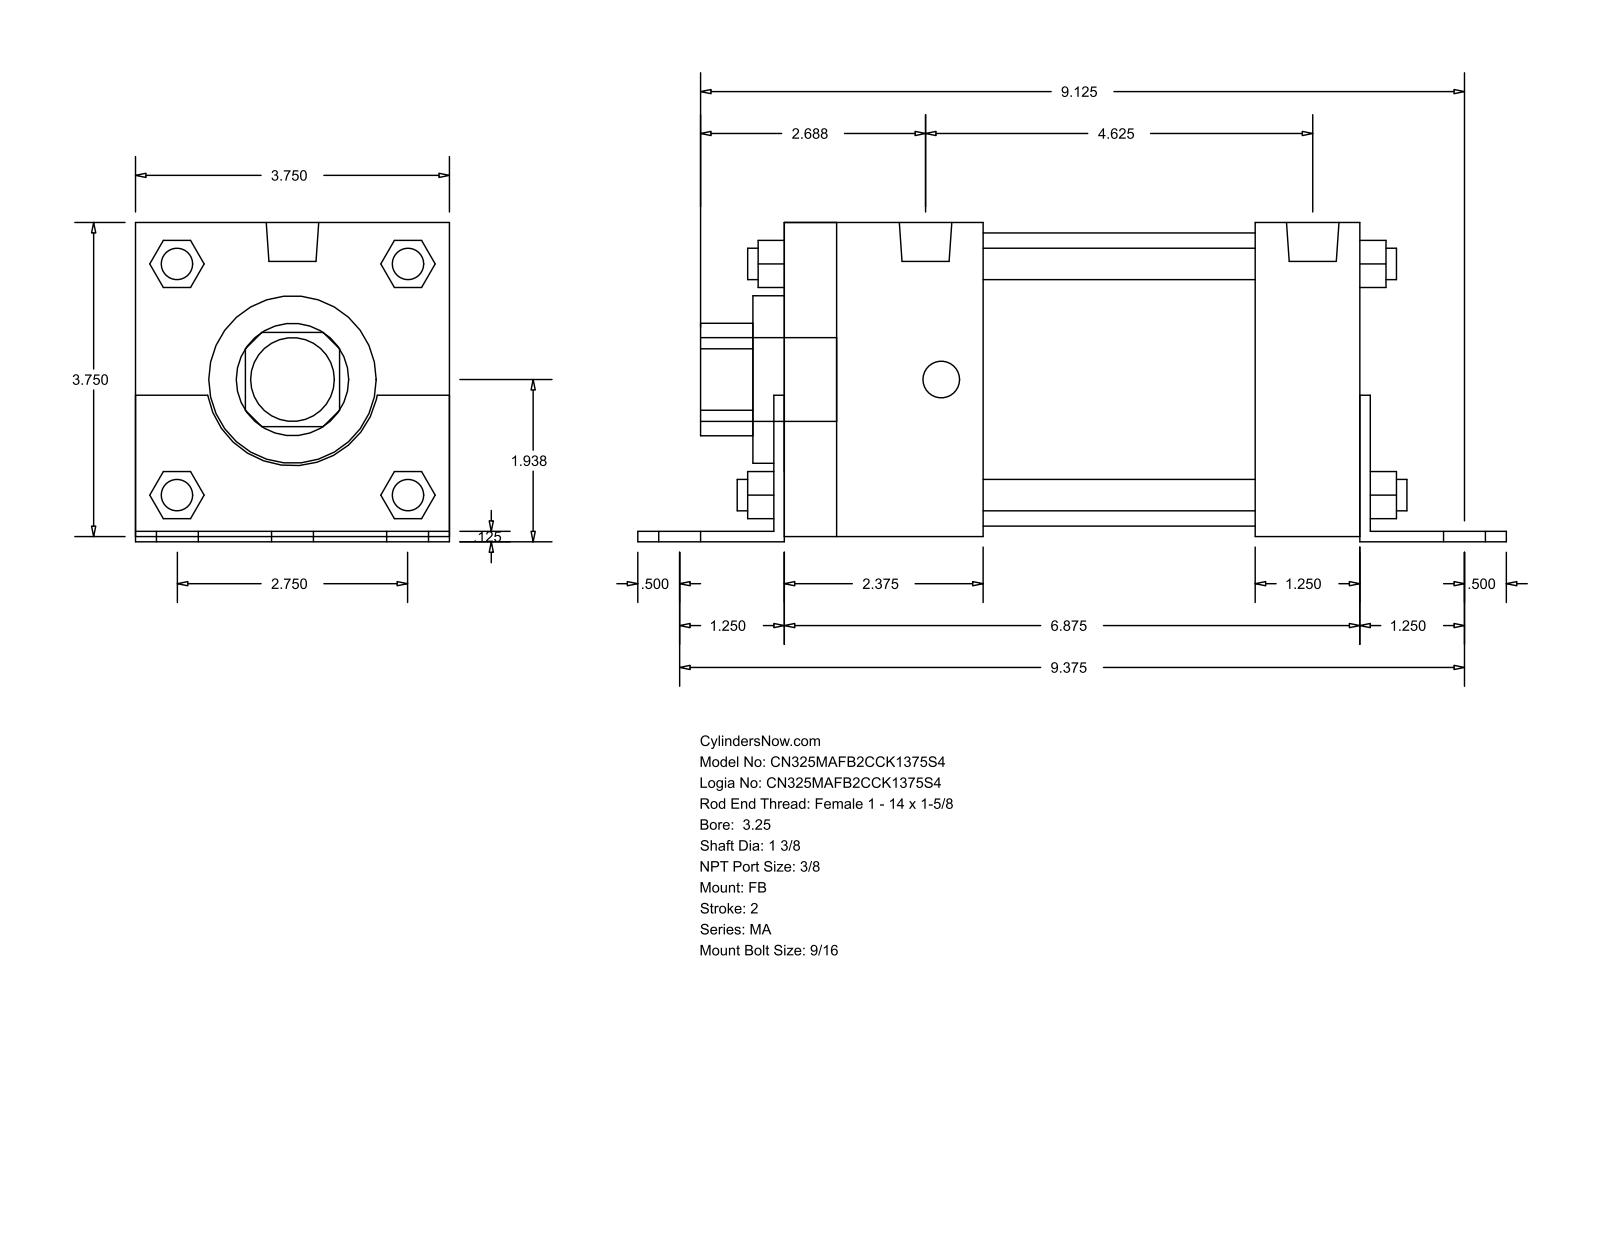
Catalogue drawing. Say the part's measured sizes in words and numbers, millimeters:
The part is named "MA_FB__0325_1.375". Its 3-D file was written by "GSSL Pune (CONFIG_CONTROL_DESIGN)". It is 0 solids with 140 faces: 105 planar, 35 cylindrical and 0 other. Overall it measures 263.52 by 96.84 by 95.25 millimeters. Round holes: 1 of diameter 34.92, 1 of diameter 50.8, 1 of diameter 88.9. Round bosses or shafts: 6 of diameter 14.29, 4 of diameter 11.11, 4 of diameter 9.53, 2 of diameter 15.93, 1 of diameter 25.4. Partial cylindrical surfaces (rounded edges, fillets, slot ends): 1 of radius 17.06, 1 of radius 26.16. The main face-to-face distances are 95.24, 3.17, 1.59, 96.83, 1.58, 93.66, 177.8, 174.63, 31.75, 60.32.
